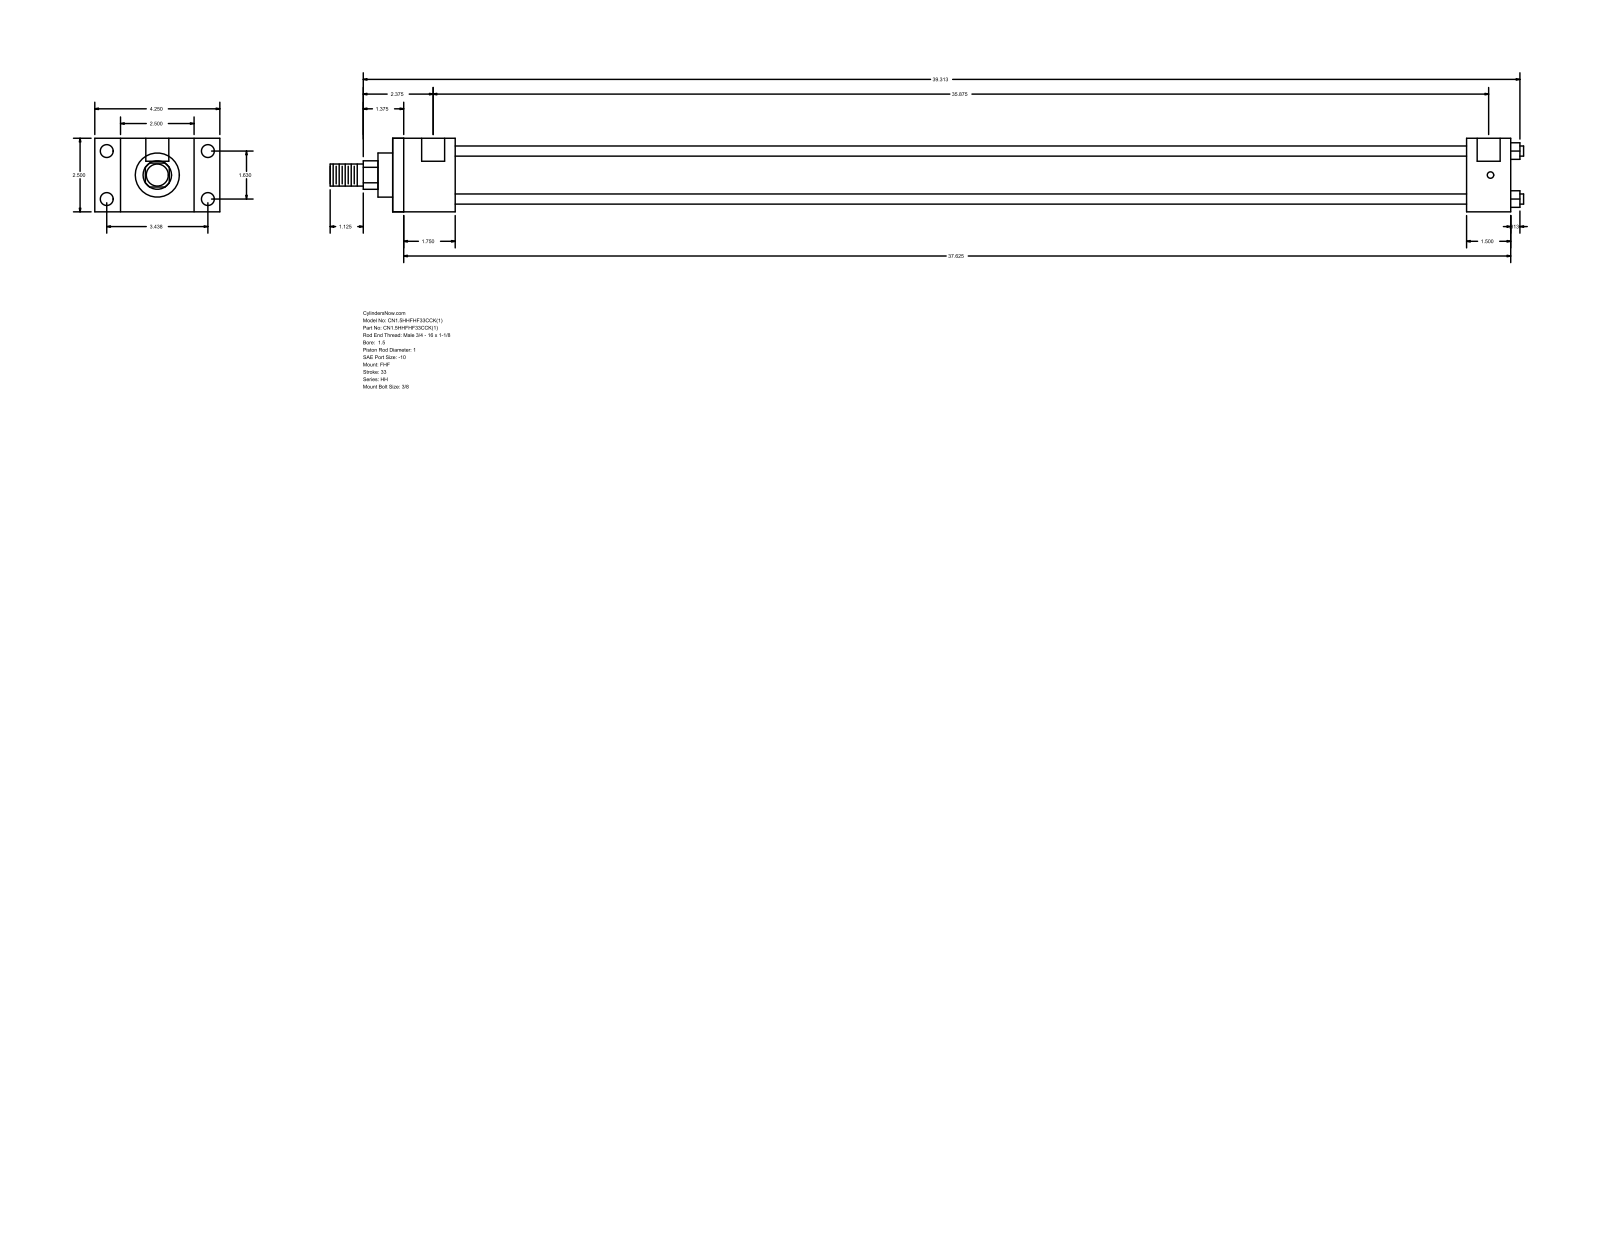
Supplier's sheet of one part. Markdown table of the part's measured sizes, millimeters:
| quantity | value |
| --- | --- |
| part name | HH_FHF__0150_1 |
| STEP written by | GSSL Pune (CONFIG_CONTROL_DESIGN) |
| units | millimeters |
| bodies | 0 solids, 88 faces (60 planar, 28 cylindrical, 0 other) |
| overall size | 1030.29 × 107.95 × 63.5 |
| round holes (diameter × count) | 5.56 × 4, 11.13 × 4, 19.84 × 2 |
| round bosses / shafts (diameter × count) | 8.76 × 4, 44.45 × 1, 38.1 × 1, 25.4 × 1, 19.05 × 1 |
| partial cylindrical surfaces (radius × count) | 12.29 × 1 |
| main face-to-face distances | 63.5, 22.23, 85.73, 53.98, 107.96, 965.2, 911.22, 38.1, 927.1, 873.12 |
| hole center spacings | 1.59, 41.4, 87.32, 96.64, 912.81, 914.4, 911.22 |
